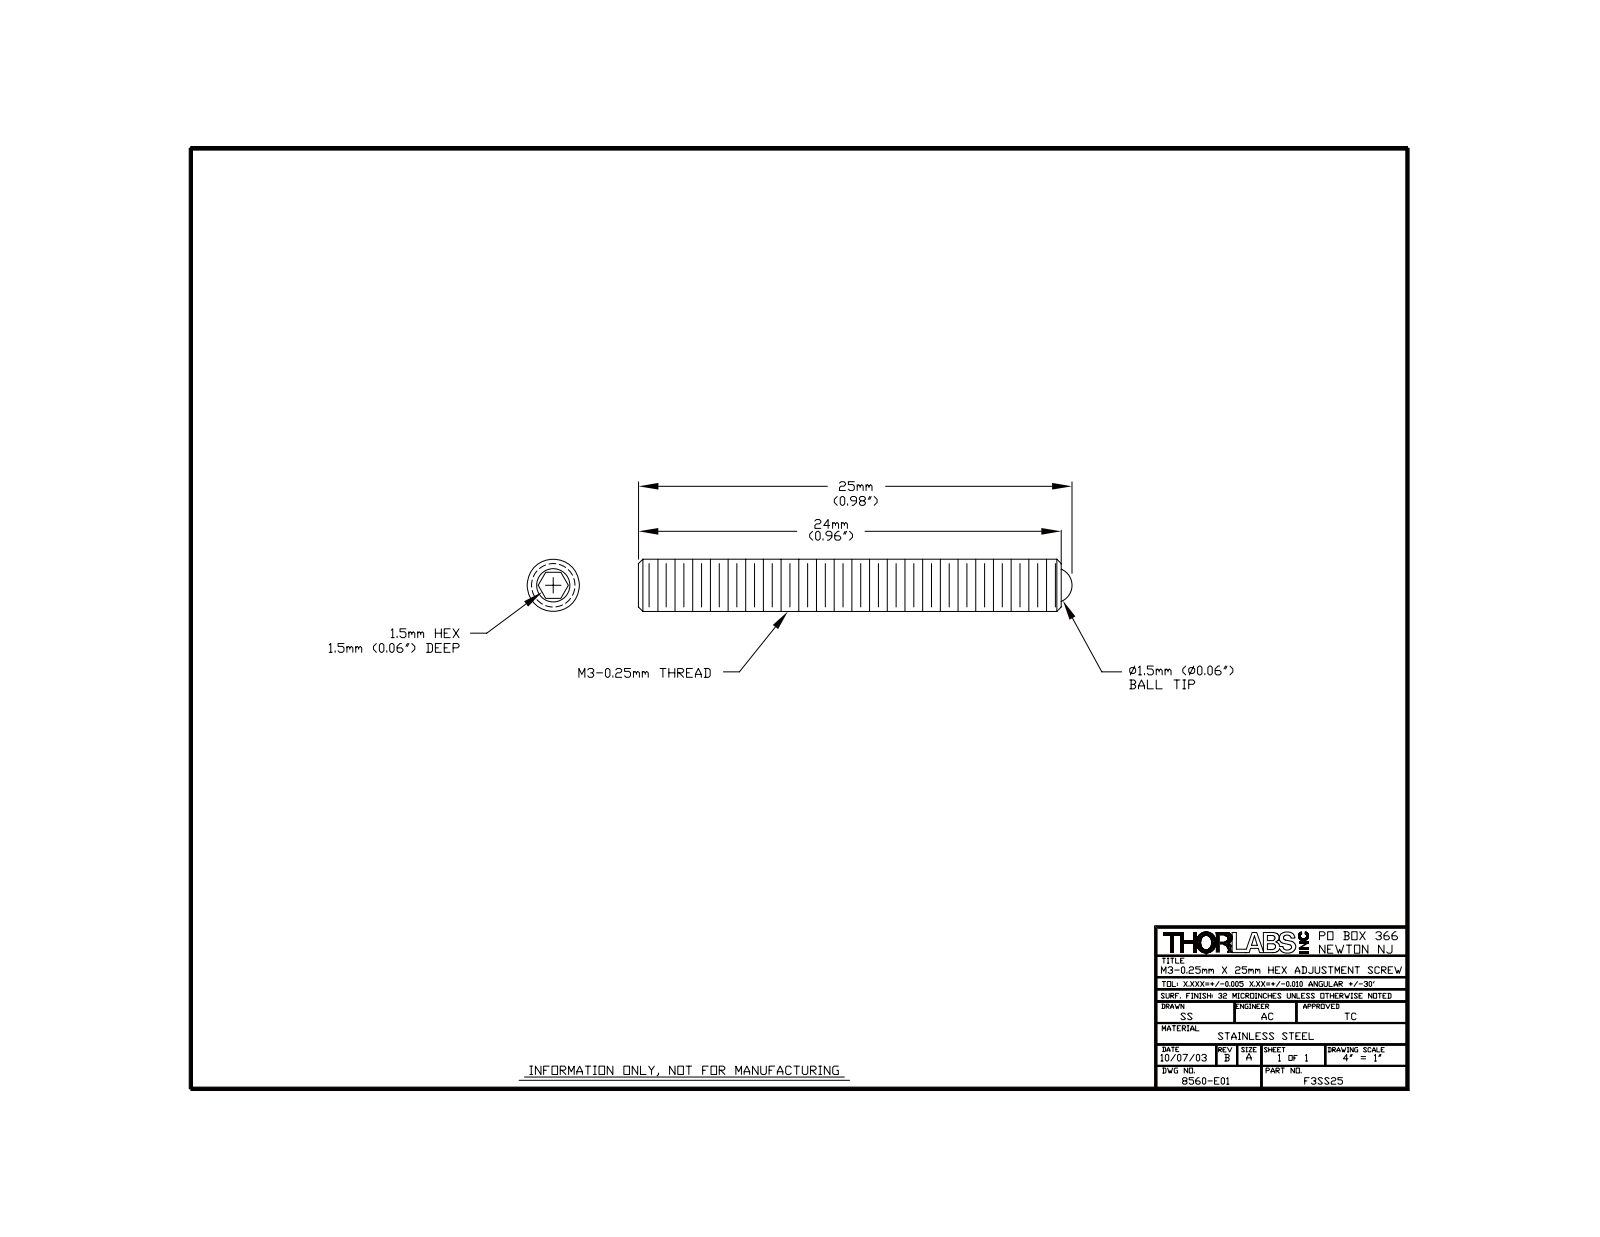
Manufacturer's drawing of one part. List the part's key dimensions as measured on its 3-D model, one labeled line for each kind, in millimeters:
Part name (STEP PRODUCT): 8560-E0W
STEP written by: SolidWorks 2011 (AUTOMOTIVE_DESIGN)
Units: millimetres
Bodies: 2 solids, 23 faces (9 planar, 4 cylindrical, 10 other)
Overall size (bounding box): 25 × 3 × 3
Volume: 160 mm³ · Surface area: 265 mm²
Round holes (diameter × count): ⌀1.6 ×1
Round bosses / shafts (diameter × count): ⌀3 ×1
Main face-to-face distances: 1.3, 1.3, 24.3, 3, 21.3
